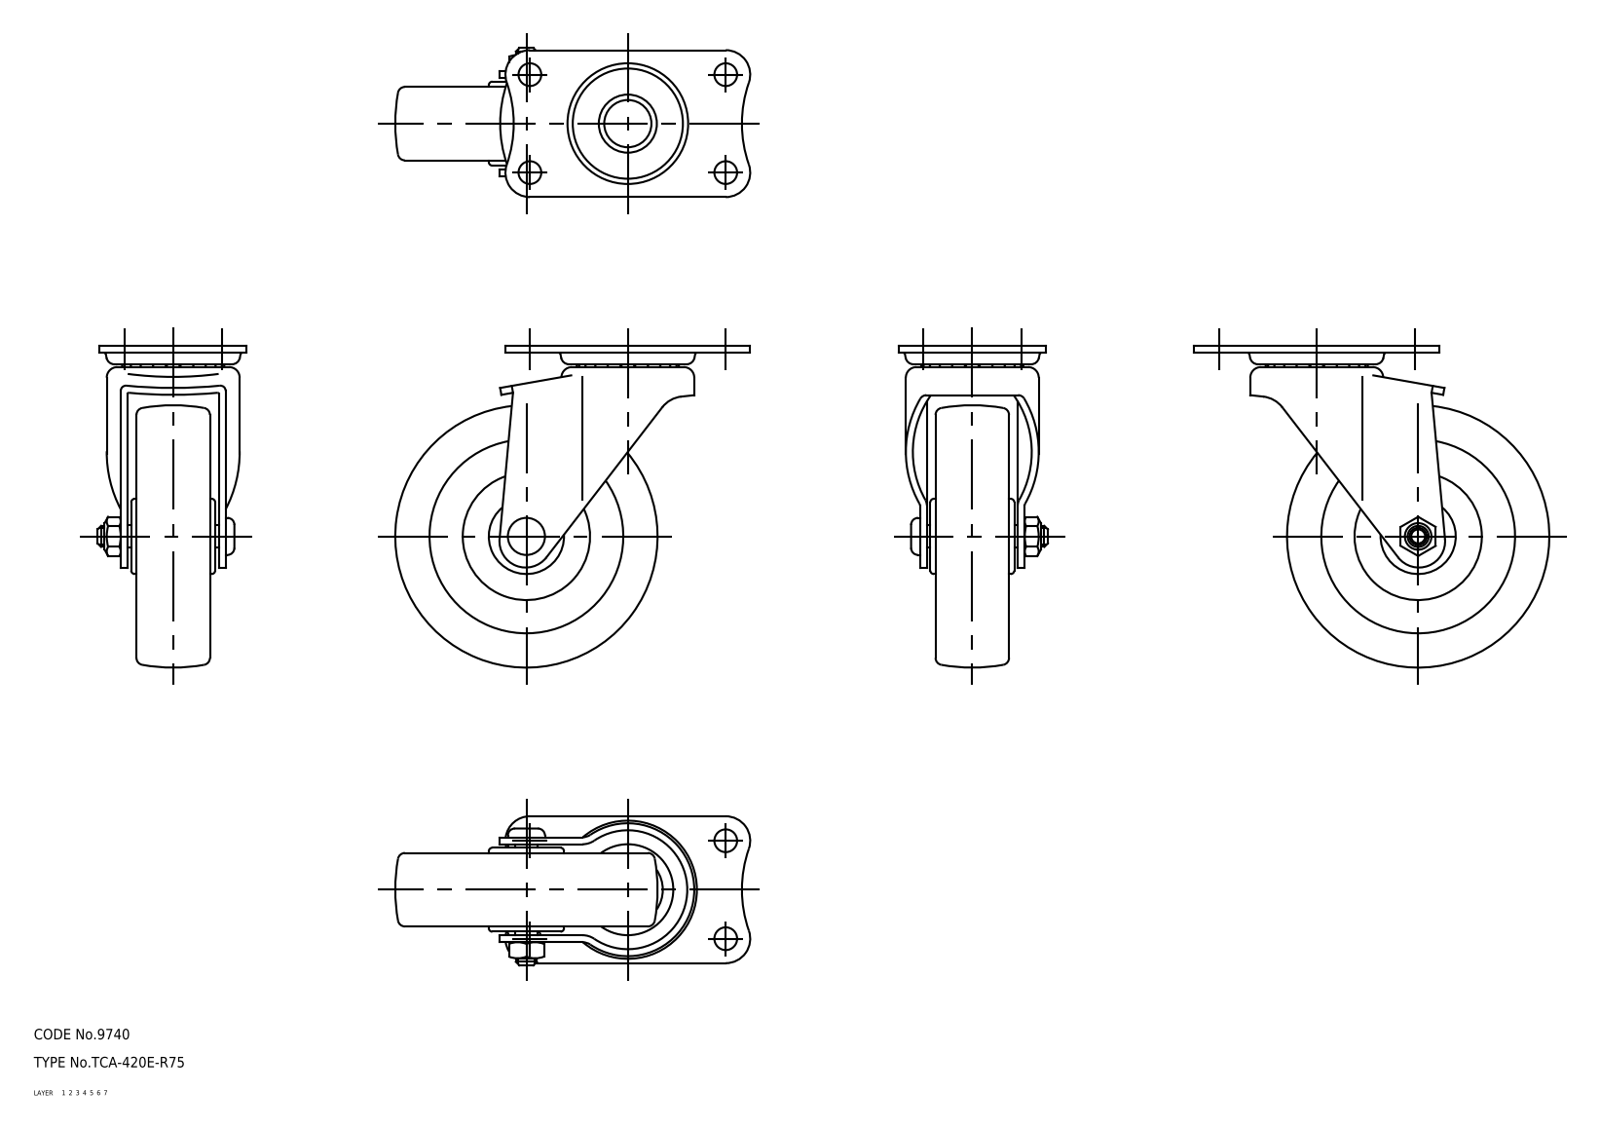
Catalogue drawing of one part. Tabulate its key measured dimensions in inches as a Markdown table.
| quantity | value |
| --- | --- |
| part name | 67213123; 67213136; 67213149; 67213162 (+1 more) |
| STEP written by | CADfix (AUTOMOTIVE_DESIGN) |
| units | inches |
| bodies | 5 solids, 235 faces (0 planar, 0 cylindrical, 235 other) |
| overall size | 3.996 × 3.622 × 1.677 |
| volume | 6.705 in³ |
| surface area | 53.57 in² |
